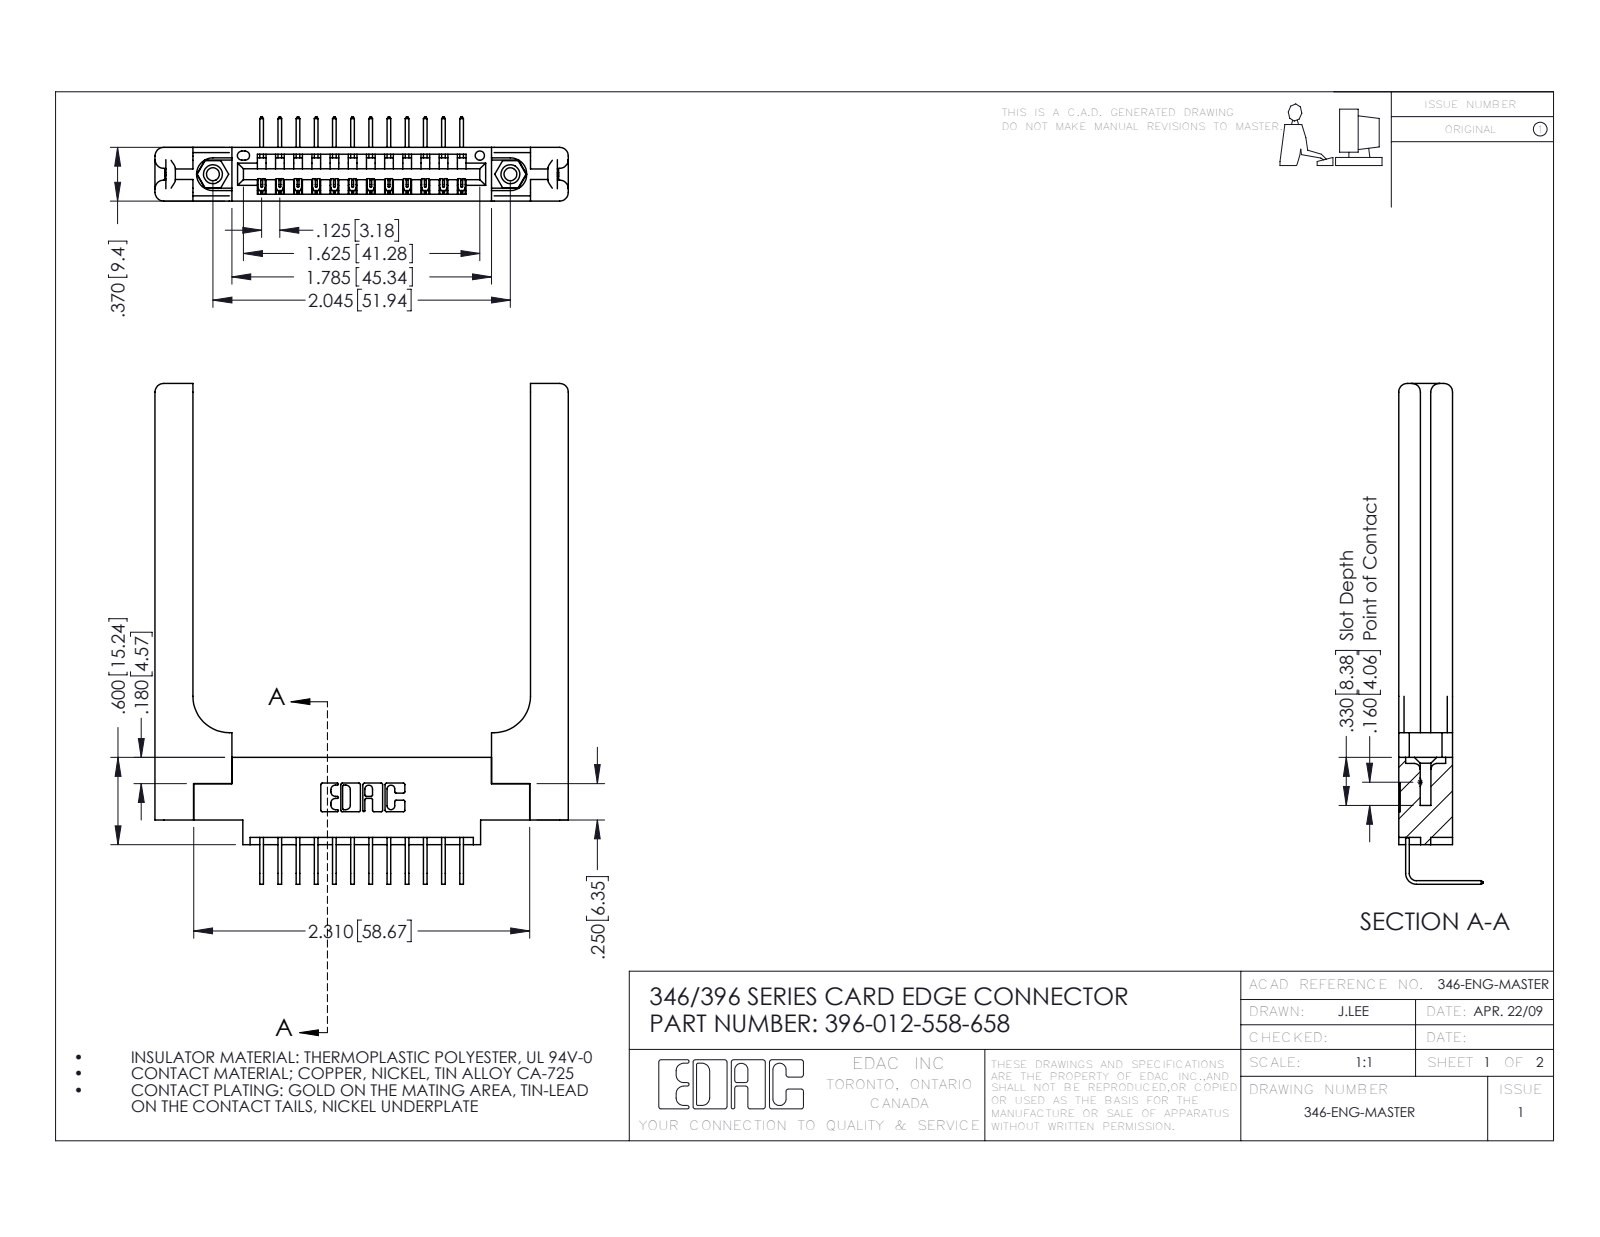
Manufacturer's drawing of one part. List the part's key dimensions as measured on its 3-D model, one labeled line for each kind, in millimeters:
Part name (STEP PRODUCT): 345-292-001_558 Tail - 2; 346-220-058_345-220-058; 346 Part_0.170 Offset - 0.156 Dia-TH; 345-250-001_345-250-001-102 (+1 more)
STEP written by: SolidWorks 2016 (CONFIG_CONTROL_DESIGN)
Units: millimetres
Bodies: 17 solids, 1102 faces (732 planar, 310 cylindrical, 60 other)
Overall size (bounding box): 87.5 × 72.2 × 14.7
Volume: 14 100 mm³ · Surface area: 13 480 mm²
Round holes (diameter × count): ⌀2.3 ×2, ⌀3.2 ×2, ⌀4 ×2, ⌀1.6 ×1
Round bosses / shafts (diameter × count): ⌀3.9 ×2
Partial cylindrical surfaces — rounded edges, fillets, slot ends (radius × count): R0.2 ×24, R0.3 ×22, R1.5 ×16, R0.2 ×6, R0.8 ×6, R0.7 ×3, R0.8 ×2, R0.8 ×2
Main face-to-face distances: 9.4, 3.8, 1.8, 3.8, 8.2, 5.6, 1.2, 6.4, 2.6, 4.4
Hole centre spacings: 6.2, 46.7, 51.9
